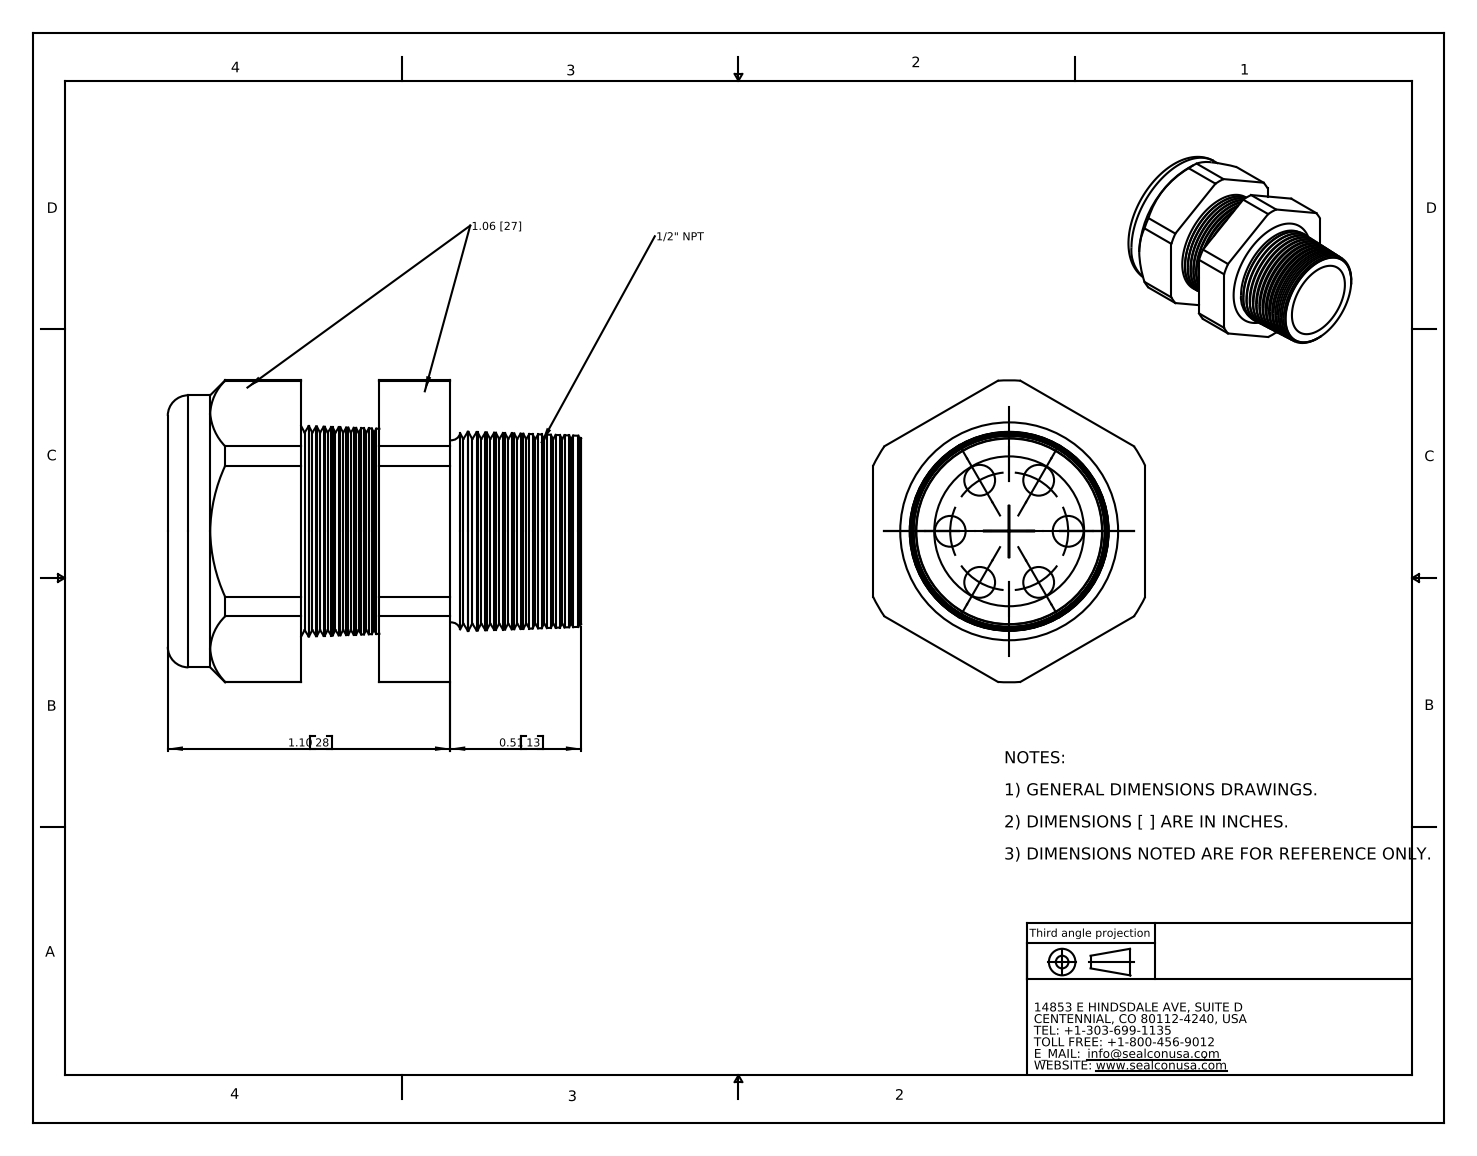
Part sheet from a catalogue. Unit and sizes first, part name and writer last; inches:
Units: inches
Overall size (bounding box): 1.61 × 1.177 × 1.06
Round holes (diameter × count): ⌀0.12 ×6, ⌀0.58 ×1, ⌀0.6 ×1
Round bosses / shafts (diameter × count): ⌀1.06 ×1
Partial cylindrical surfaces — rounded edges, fillets, slot ends (radius × count): R0.588 ×1
Main face-to-face distances: 1.06, 0.305, 0.58, 0.276, 0.52, 0.824, 1.1, 0.35, 0.17, 0.474
Hole centre spacings: 0.23, 0.23, 0.398, 0.398, 0.459, 0.46
Volume: 0.741 in³ · Surface area: 13.22 in²
Bodies: 2 solids, 210 faces (20 planar, 32 cylindrical, 158 other)
Part name (STEP PRODUCT): CD16N8-BK
STEP written by: SolidWorks 2007 (CONFIG_CONTROL_DESIGN)
